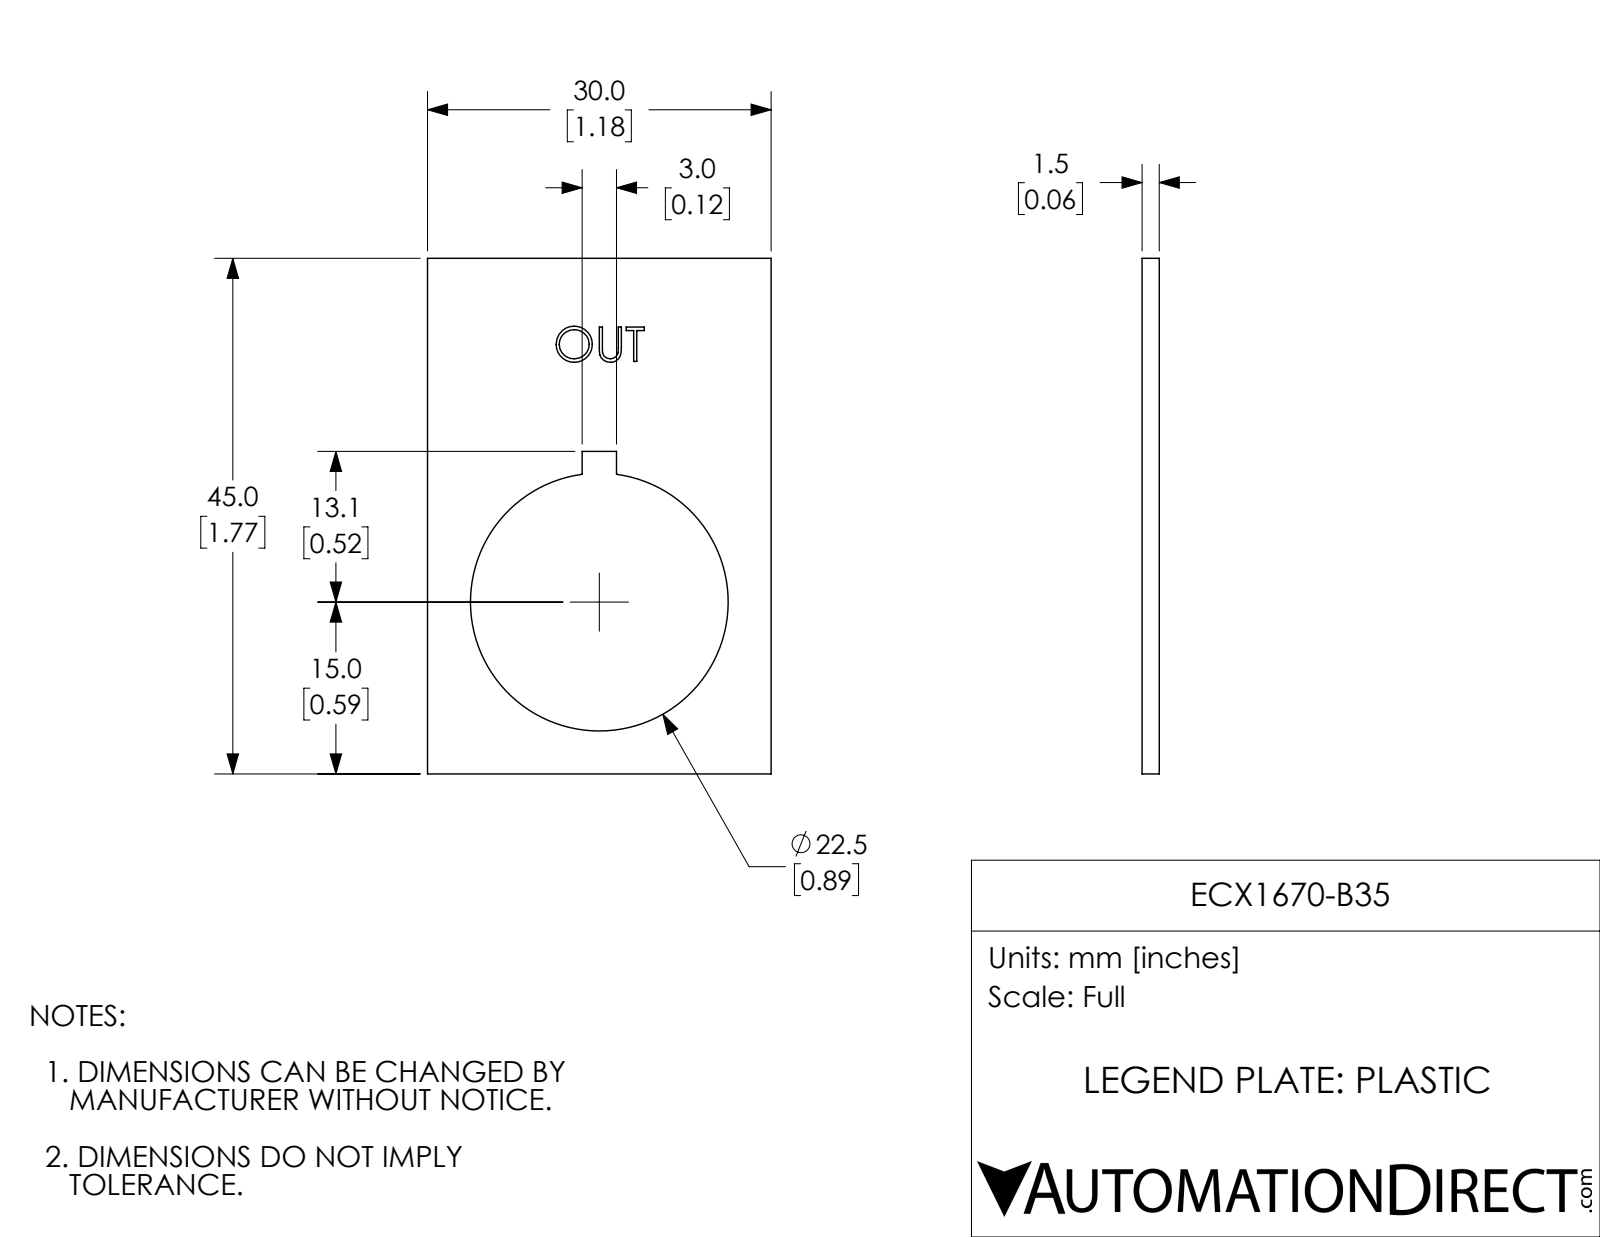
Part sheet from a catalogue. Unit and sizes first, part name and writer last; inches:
Units: inches
Overall size (bounding box): 1.772 × 1.181 × 0.059
Round holes (diameter × count): ⌀0.886 ×1
Main face-to-face distances: 0.059, 1.181, 1.772, 0.531, 0.65, 0.058, 1.108, 0.663, 0.118, 0.07
Volume: 0.087 in³ · Surface area: 3.459 in²
Bodies: 1 solid, 45 faces (27 planar, 3 cylindrical, 15 other)
Part name (STEP PRODUCT): ECX1670-B35
STEP written by: SolidWorks 2017 (AUTOMOTIVE_DESIGN)
